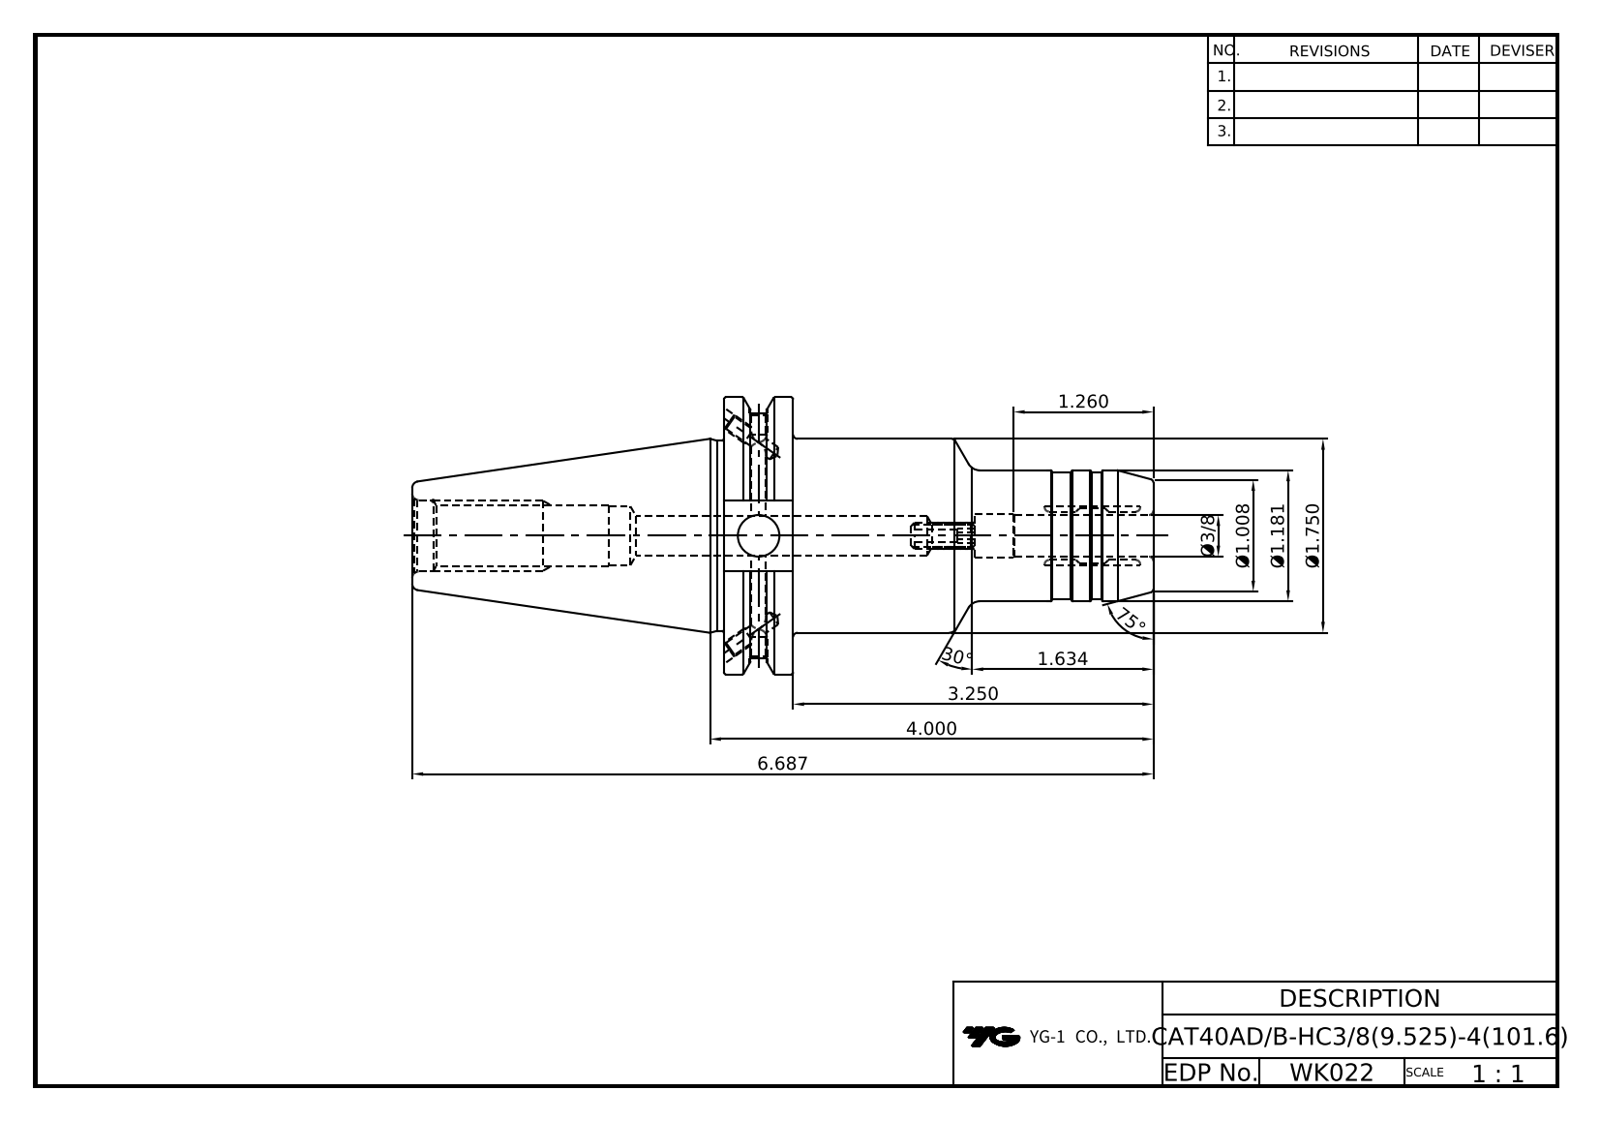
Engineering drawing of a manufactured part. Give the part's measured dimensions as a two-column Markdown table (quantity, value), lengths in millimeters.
| quantity | value |
| --- | --- |
| part name | CAT40ADB-SHANK |
| STEP written by | CREO PARAMETRIC BY PTC INC, 2018500 (CONFIG_CONTROL_DESIGN) |
| units | millimeters |
| bodies | 1 solid, 143 faces (35 planar, 36 cylindrical, 72 other) |
| overall size | 169.88 × 63.5 × 60.84 |
| volume | 188 667 mm³ |
| surface area | 32 853 mm² |
| round holes (diameter × count) | 9.53 × 2, 6 × 1, 9 × 1, 10 × 1, 13.49 × 1, 15.88 × 1, 16.3 × 1 |
| round bosses / shafts (diameter × count) | 63.5 × 1, 56.3 × 1, 44.45 × 1, 43.6 × 1, 30 × 1, 29 × 1 |
| main face-to-face distances | 15.9, 98.45, 82.55, 47.6, 71.42, 87.32, 169.87, 16.38, 77.47, 6.05 |
